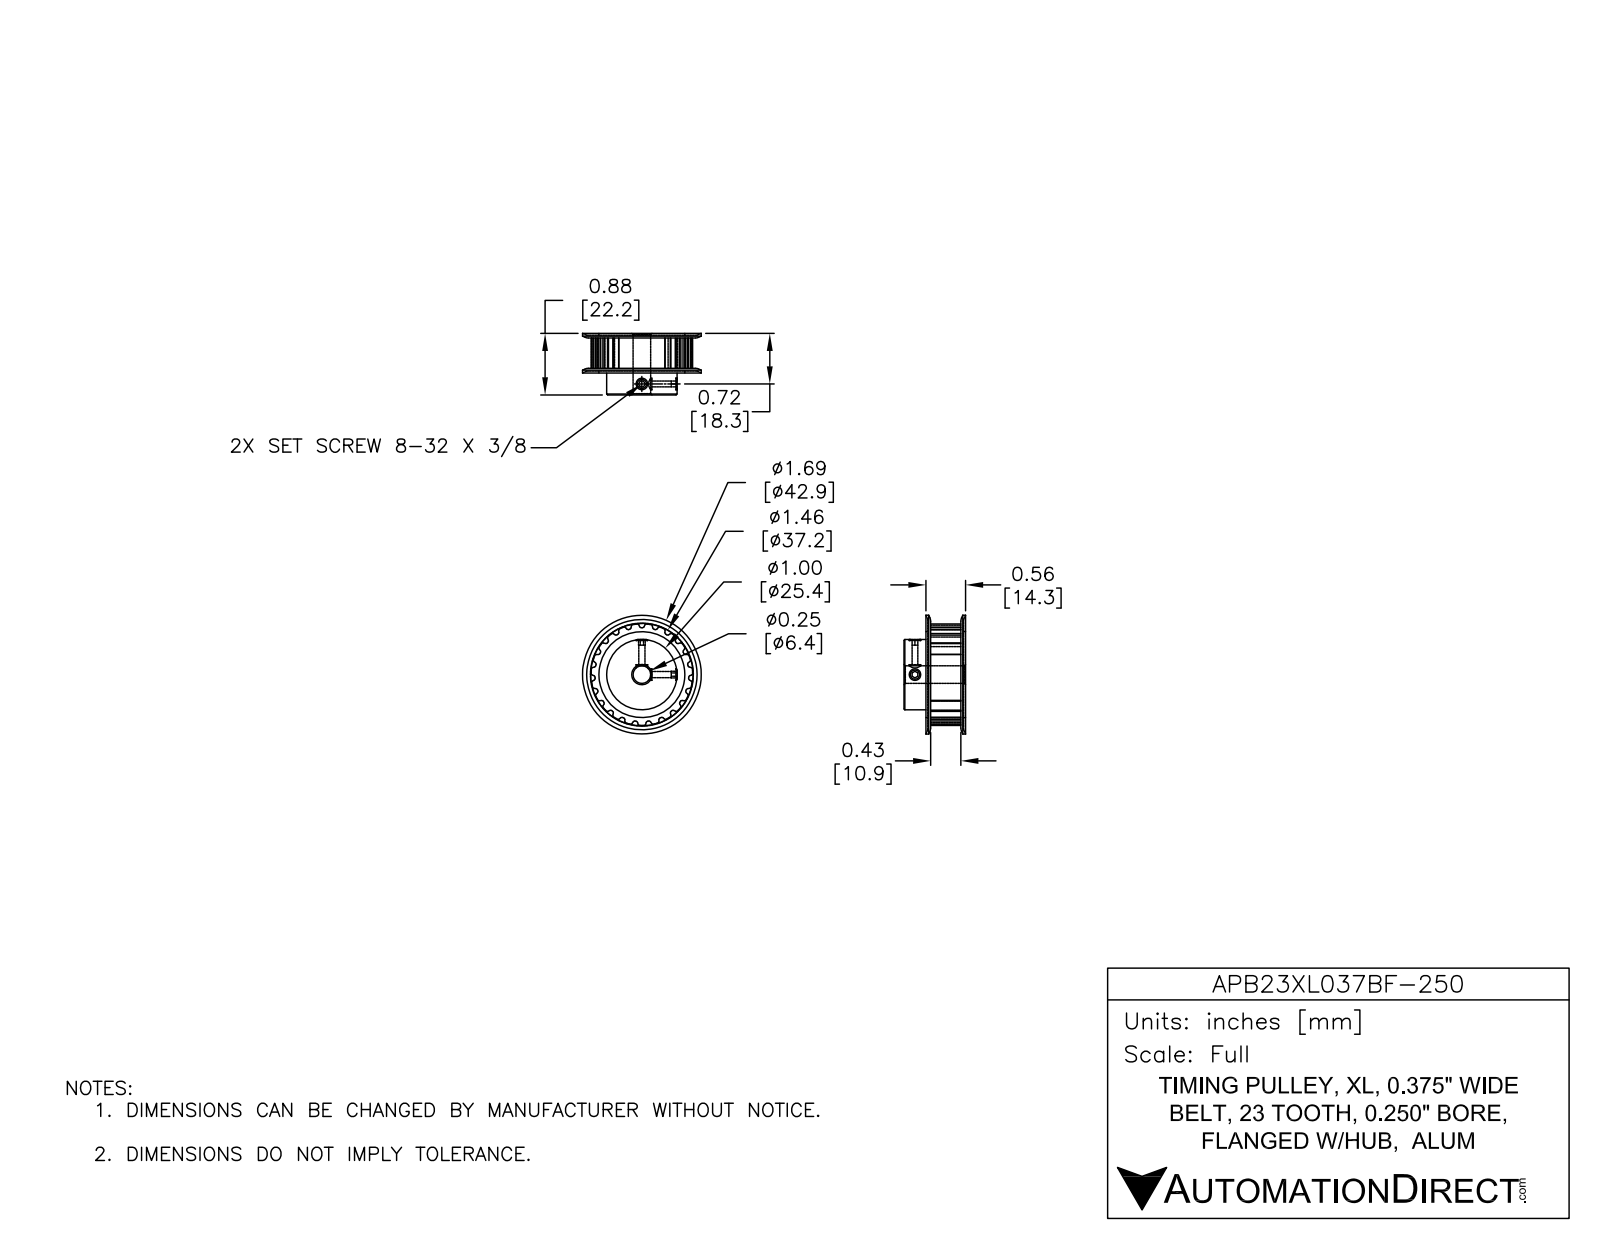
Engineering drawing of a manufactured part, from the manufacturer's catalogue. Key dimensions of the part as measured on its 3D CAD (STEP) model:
Part name (STEP PRODUCT): APB23XL037BF-250
STEP written by: SolidWorks 2014 (AUTOMOTIVE_DESIGN)
Units: millimetres
Bodies: 1 solid, 239 faces (75 planar, 142 cylindrical, 22 other)
Overall size (bounding box): 42.88 × 42.88 × 22.23
Volume: 17 986 mm³ · Surface area: 6 935 mm²
Round holes (diameter × count): ⌀2.23 ×2, ⌀6.35 ×1
Round bosses / shafts (diameter × count): ⌀27 ×1
Partial cylindrical surfaces — rounded edges, fillets, slot ends (radius × count): R0.38 ×92, R16.94 ×1
Main face-to-face distances: 0.83, 12.57, 22.23, 13.4, 8.83, 21.4, 11.74, 9.66, 1.65, 0.82
